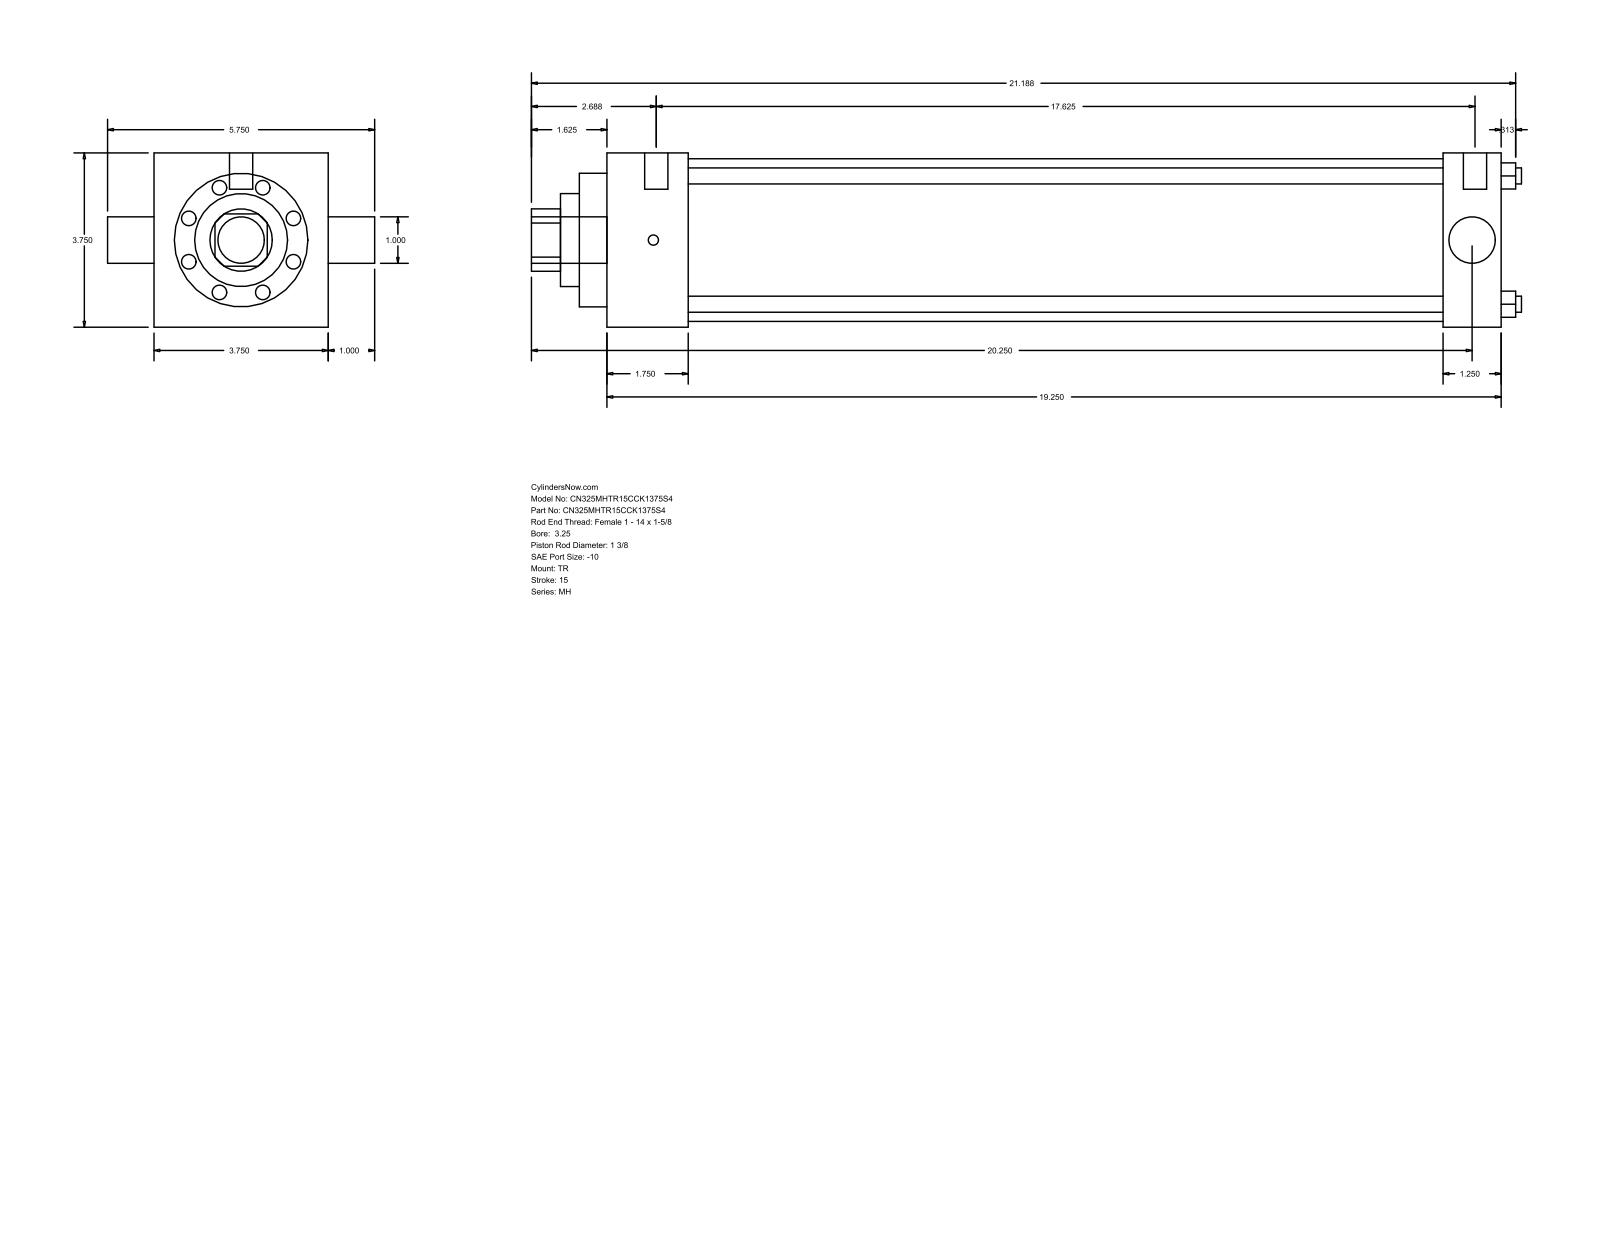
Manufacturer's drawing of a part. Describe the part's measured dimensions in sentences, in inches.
The part is named "MH_TR__0325_1.375". Its 3-D file was written by "GSSL Pune (CONFIG_CONTROL_DESIGN)". It is 0 solids with 86 faces: 61 planar, 25 cylindrical and 0 other. Overall it measures 21.313 by 5.75 by 3.75 inches. Round holes: 4 of diameter 0.345, 1 of diameter 1, 1 of diameter 1.375, 1 of diameter 2, 1 of diameter 2.875, 1 of diameter 3.5. Round bosses or shafts: 3 of diameter 0.219, 2 of diameter 0.5, 1 of diameter 1. Partial cylindrical surfaces (rounded edges, fillets, slot ends): 1 of radius 0.672. The main face-to-face distances are 3.75, 19.25, 1.75, 18, 16.25, 17.5, 1.25, 0.594, 2.344, 18.594. The hole center spacings are 1.952, 2.76, 3.903.
